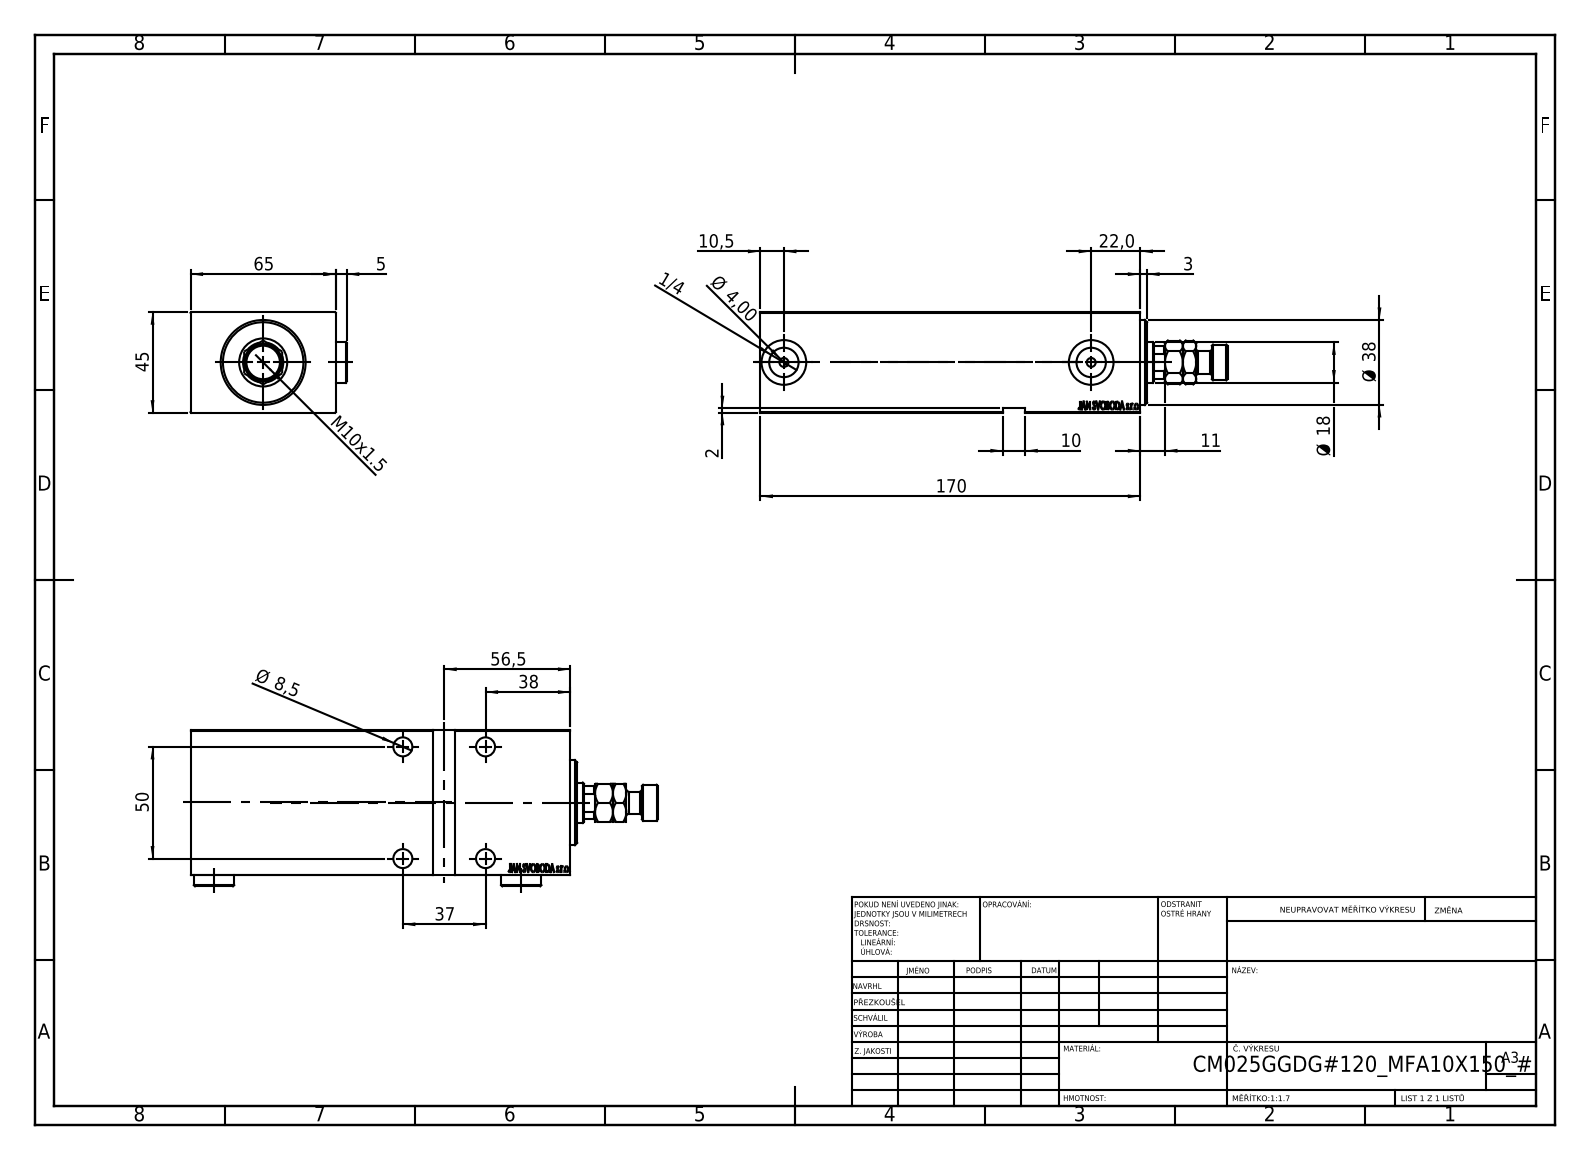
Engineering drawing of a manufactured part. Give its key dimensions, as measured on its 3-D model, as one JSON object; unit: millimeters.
{"part_name": "V450CM_G_VCP; V450CM_VC_G; MFA; V450CM_G_Body (+1 more)", "step_written_by": "SolidWorks 2019 (CONFIG_CONTROL_DESIGN)", "units": "millimeters", "bodies": {"solids": 6, "faces": 965, "planar": 461, "cylindrical": 74, "other": 430}, "overall_size": [209, 69.9, 45], "volume_mm3": 457492, "surface_area_mm2": 83640, "round_holes": [[8.5, 5], [13.5, 4], [4, 2], [13.16, 2], [20, 2], [18, 1], [21.5, 1], [25, 1], [27, 1], [35, 1]], "round_bosses_or_shafts": [[18, 2], [38, 1], [16, 1], [10, 1]], "partial_cylinders_radius": [[8.5, 1]], "face_to_face_distances": [45, 65, 170, 6, 64.9, 159, 5, 8, 164, 11], "hole_center_spacings": [37, 50, 62.2, 137.5]}
